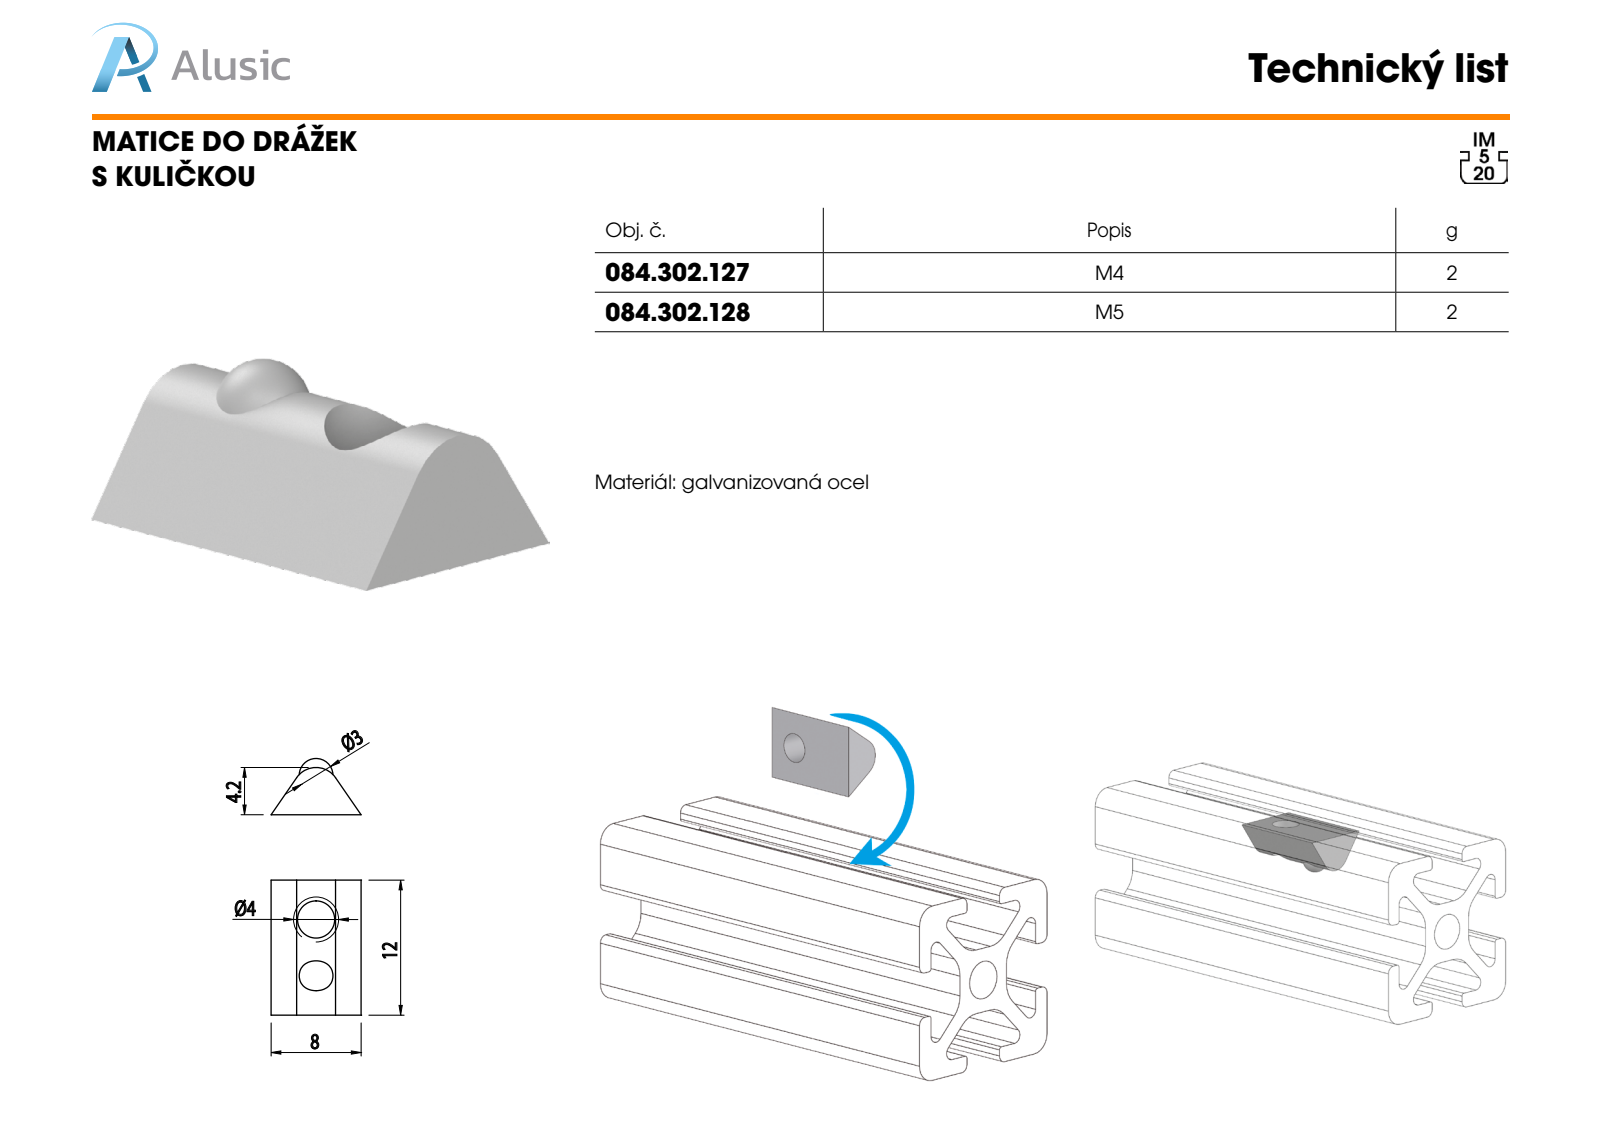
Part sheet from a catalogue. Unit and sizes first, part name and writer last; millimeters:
Units: millimetres
Overall size (bounding box): 12 × 8 × 5
Round holes (diameter × count): ⌀4.2 ×1
Partial cylindrical surfaces — rounded edges, fillets, slot ends (radius × count): R3 ×2
Main face-to-face distances: 12
Volume: 229 mm³ · Surface area: 335 mm²
Bodies: 2 solids, 11 faces (5 planar, 4 cylindrical, 2 other)
Part name (STEP PRODUCT): Dado a culla; Sfera; 084.302.127
STEP written by: SolidWorks 2016 (CONFIG_CONTROL_DESIGN)
